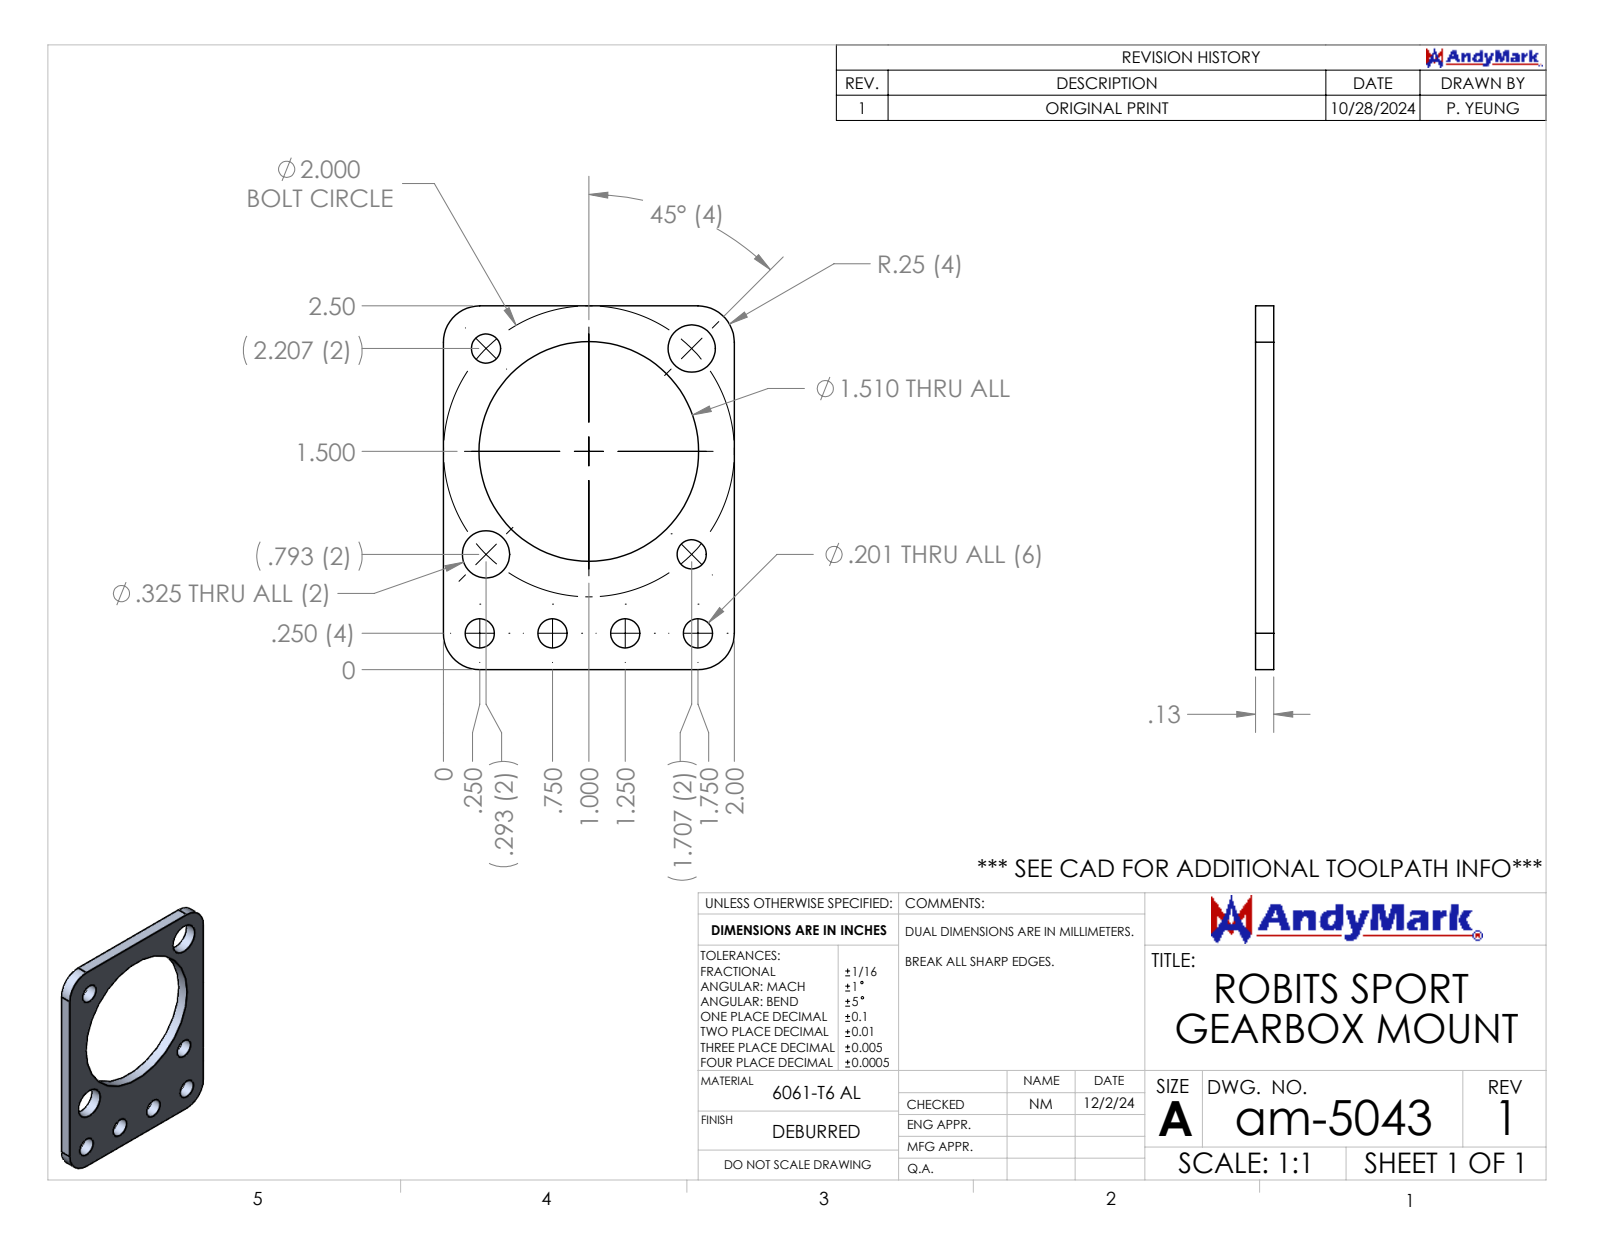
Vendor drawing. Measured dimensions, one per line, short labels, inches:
name: am-5043 Robits Sport Gearbox Mount
written by: SolidWorks 2024 (AUTOMOTIVE_DESIGN)
unit: in
bodies: 1 solid, 28 faces (6 planar, 22 cylindrical, 0 other)
size: 2.5 × 2 × 0.125
volume: 0.35 in³; area: 7.992 in²
holes: 6× ⌀0.201, 2× ⌀0.325, 1× ⌀1.51
rounds: 4× R0.25
face distances: 0.125, 2, 2.5
hole spacings: 1, 1.414, 0.5, 0.544, 0.71, 1.1, 1.275, 1.458
